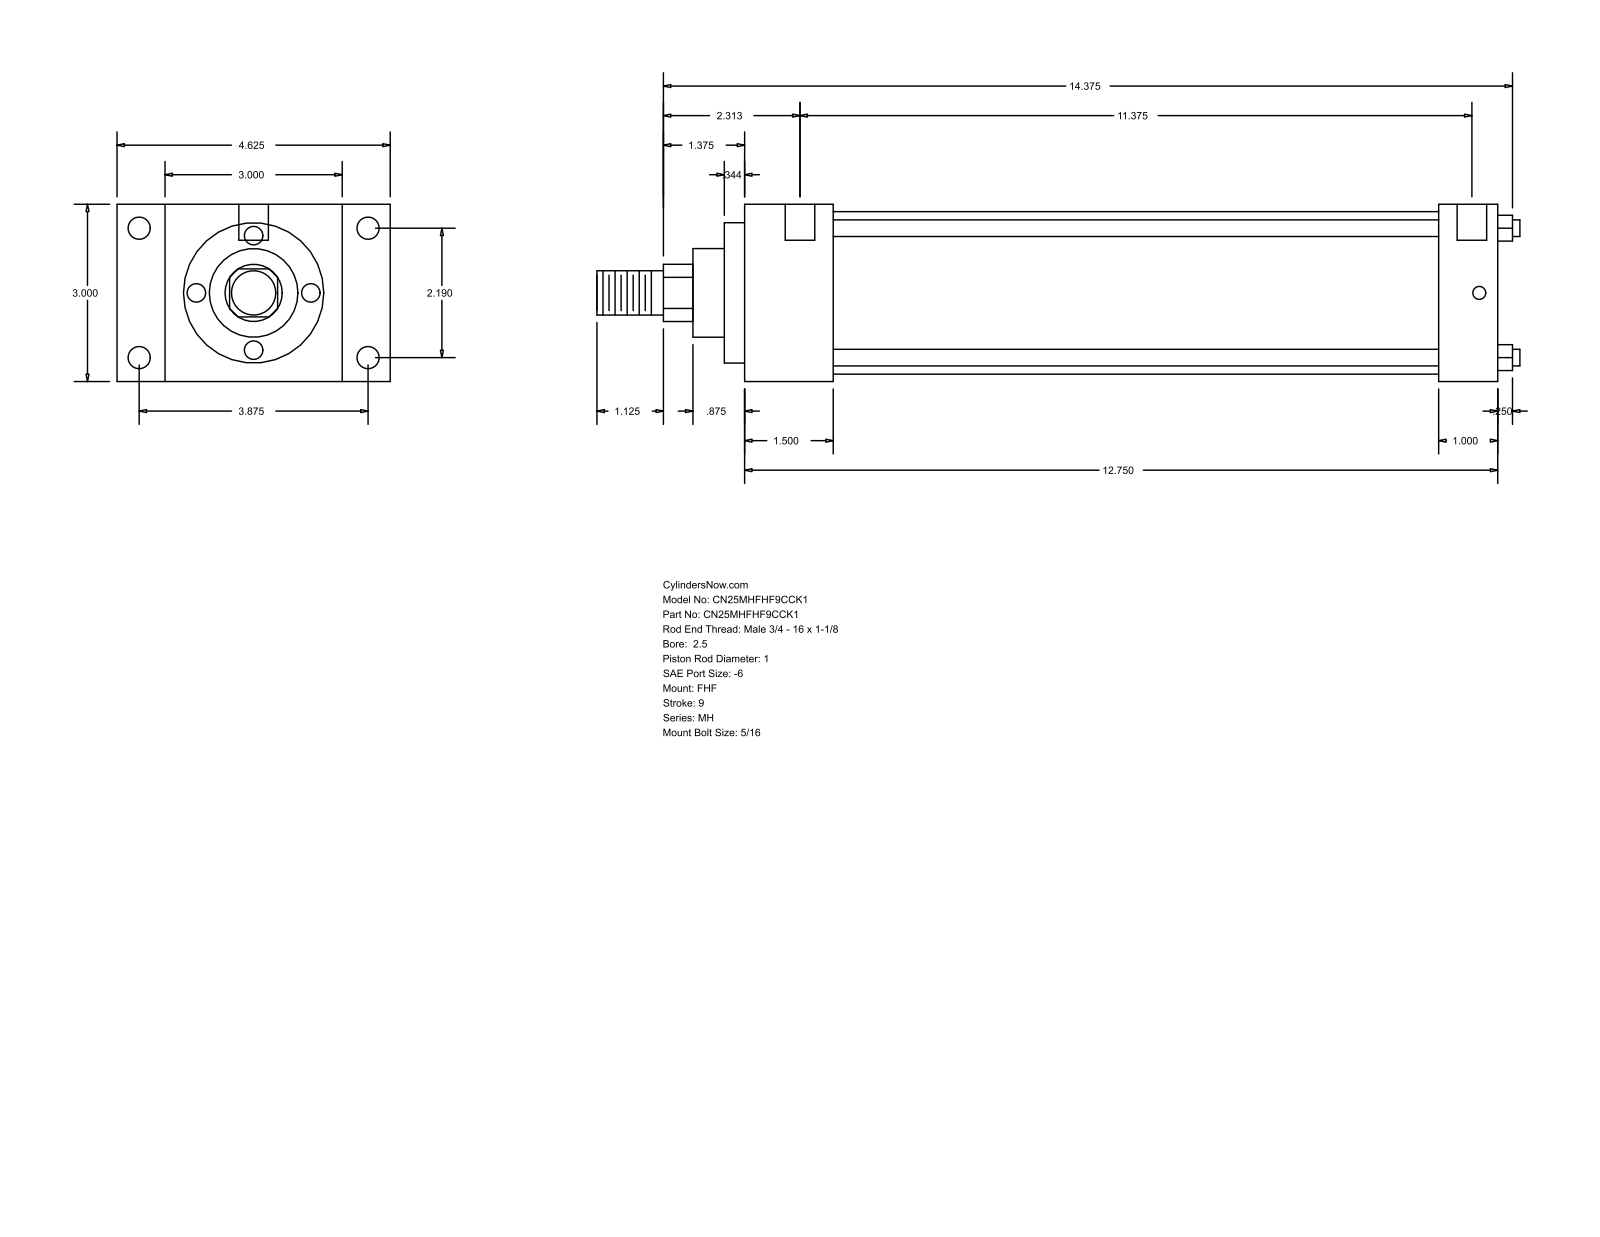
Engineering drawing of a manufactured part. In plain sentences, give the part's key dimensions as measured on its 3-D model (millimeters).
The part is named "MH_FHF__0250_1". Its 3-D file was written by "GSSL Pune (CONFIG_CONTROL_DESIGN)". It is 0 solids with 90 faces: 61 planar, 29 cylindrical and 0 other. Overall it measures 396.88 by 117.47 by 76.2 millimeters. Round holes: 4 of diameter 5.56, 4 of diameter 9.53, 2 of diameter 12.7. Round bosses or shafts: 4 of diameter 7.14, 1 of diameter 69.85, 1 of diameter 60.33, 1 of diameter 38.1, 1 of diameter 25.4, 1 of diameter 19.05. Partial cylindrical surfaces (rounded edges, fillets, slot ends): 1 of radius 12.29. The main face-to-face distances are 76.2, 323.85, 38.11, 285.74, 20.64, 96.84, 117.48, 25.39, 298.46, 260.35. The hole center spacings are 55.62, 98.42, 113.05, 296.86, 3.18, 4.76, 288.92, 292.1.
